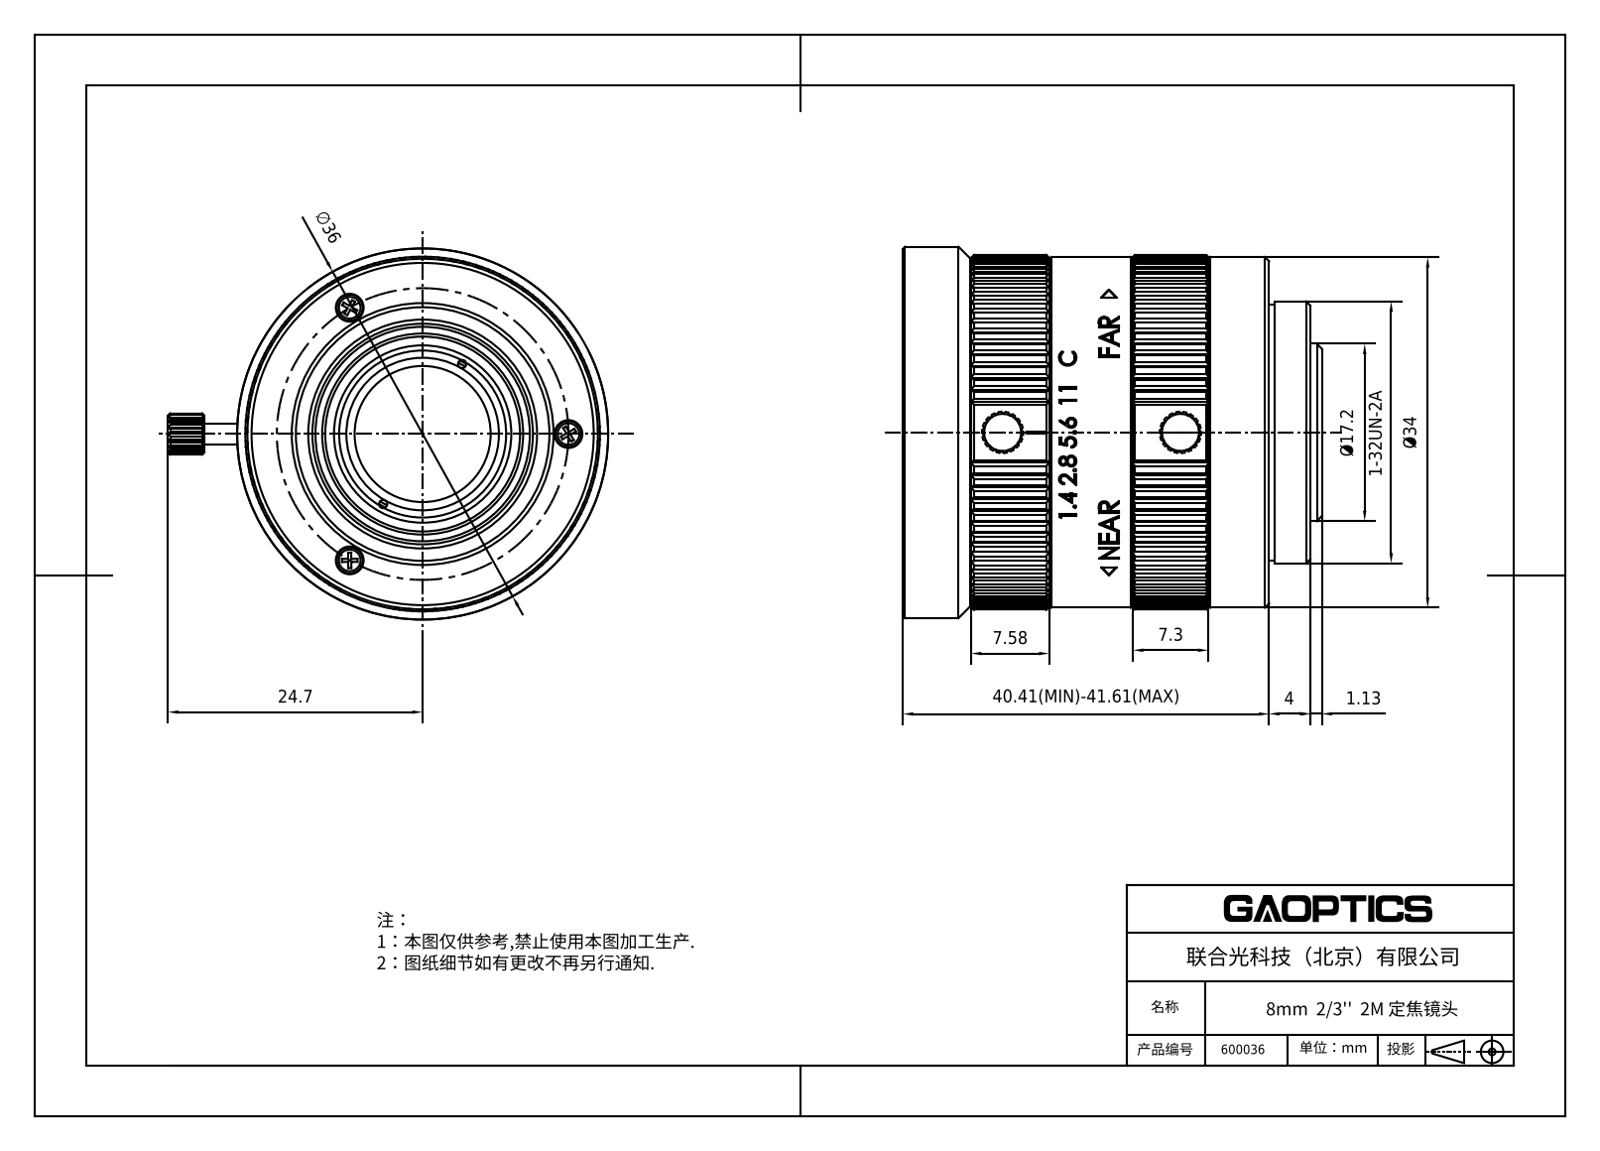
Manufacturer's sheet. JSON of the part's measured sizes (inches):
{"part_name": "600036", "step_written_by": "SolidWorks 2020 (CONFIG_CONTROL_DESIGN)", "units": "inches", "bodies": {"solids": 4, "faces": 1596, "planar": 656, "cylindrical": 356, "other": 584}, "overall_size": [1.595, 1.568, 1.417], "volume_in3": 1.865, "surface_area_in2": 20.98, "round_holes": [[0.063, 4], [0.106, 3], [0.031, 2], [0.059, 1], [0.098, 1], [0.52, 1], [0.551, 1], [0.608, 1], [0.609, 1], [0.63, 1], [0.744, 1], [0.843, 1]], "round_bosses_or_shafts": [[0.098, 3], [0.079, 2], [1.417, 1], [1.354, 1], [1.339, 1], [1.295, 1], [1.28, 1], [1.272, 1]], "partial_cylinders_radius": [[0.079, 8], [0.043, 1], [0.626, 1], [0.665, 1]], "face_to_face_distances": [1.28, 0.143, 1.138, 0.016, 0.133, 1.139, 1.415, 1.272, 0.134, 1.265], "hole_center_spacings": [0.307, 0.557, 0.965, 0.259, 0.287, 0.431, 0.535, 0.557]}
